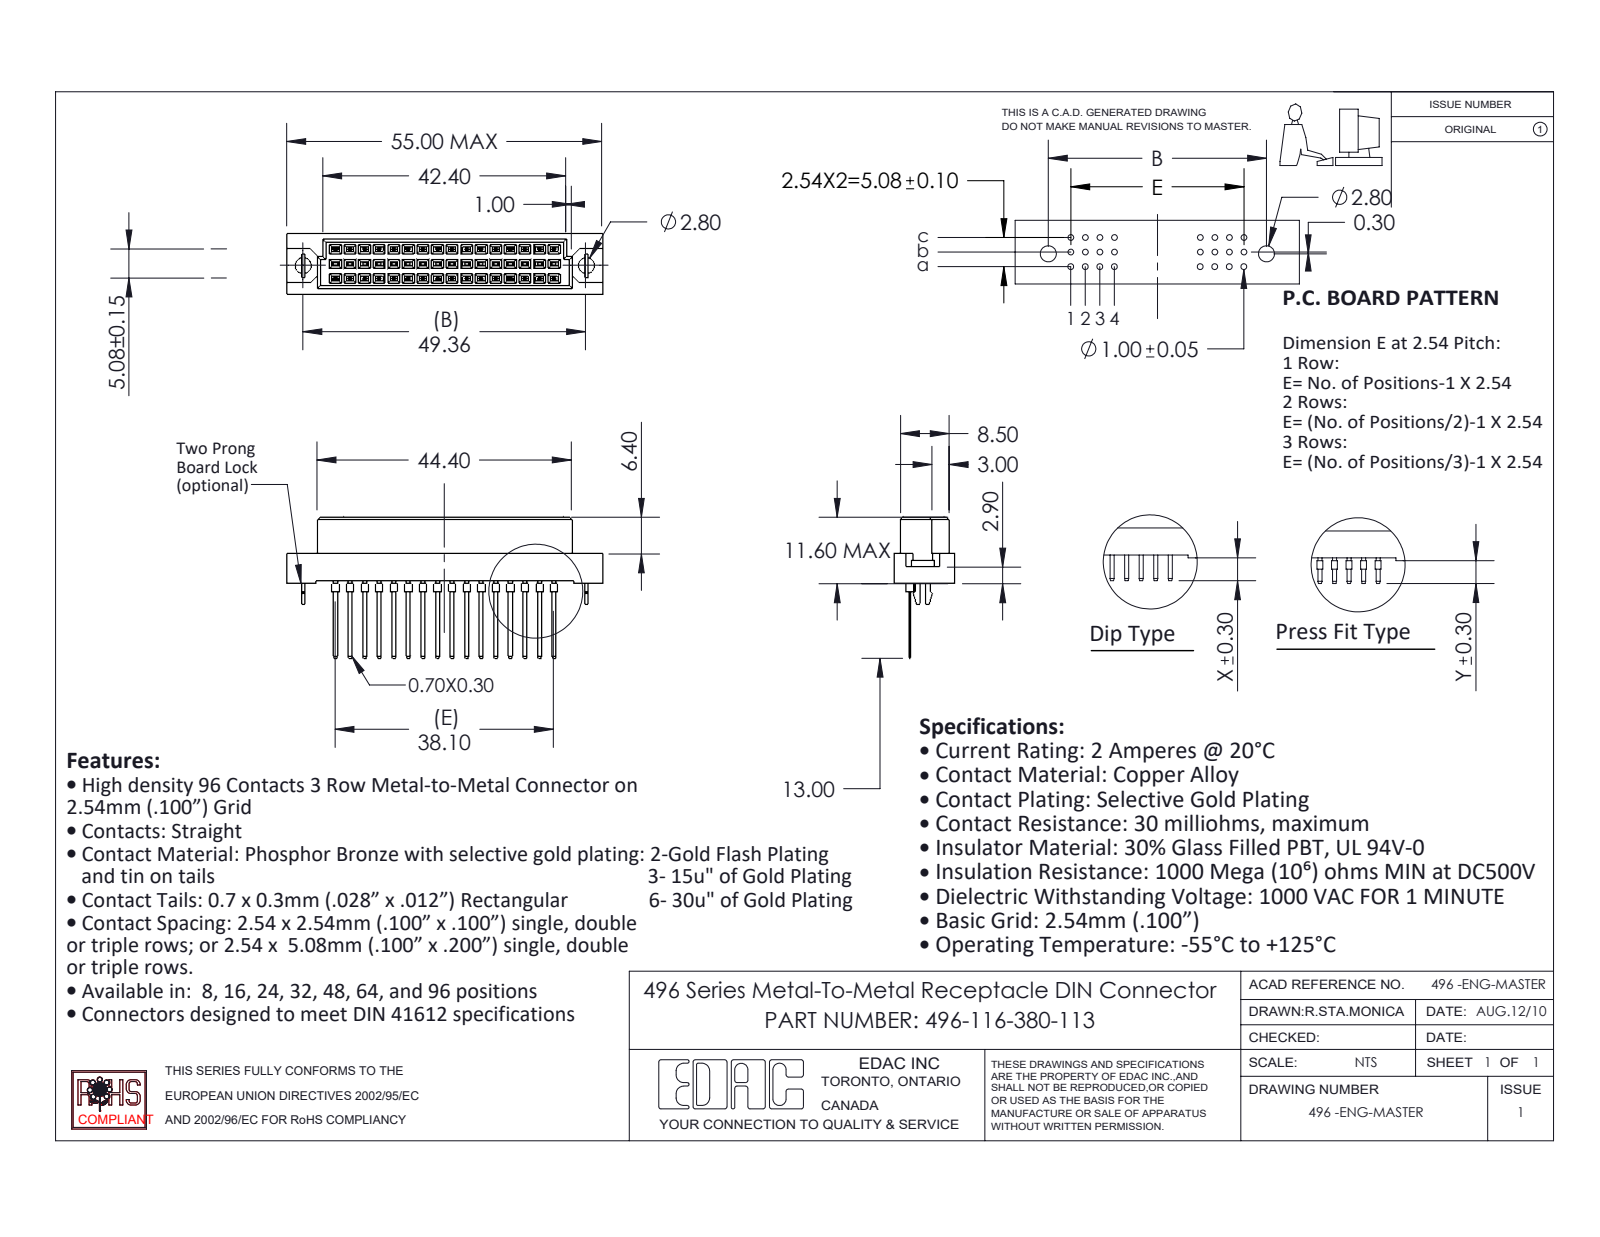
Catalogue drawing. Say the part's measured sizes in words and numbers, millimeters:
The part is named "496 Bore-lock; 496-290_80; 496-116-380-113; 496 Part_48". Its 3-D file was written by "SolidWorks 2020 (CONFIG_CONTROL_DESIGN)". It is 19 solids with 990 faces: 952 planar, 38 cylindrical and 0 other. Overall it measures 55 by 24.6 by 10.6 millimeters. Its volume is 4 684 cubic millimeters and its surface area 4 935 square millimeters. Round holes: 2 of diameter 2.8. Round bosses or shafts: 16 of diameter 1. Partial cylindrical surfaces (rounded edges, fillets, slot ends): 1 of radius 0.53. The main face-to-face distances are 2.54, 1.05, 9.55, 5.08, 0.81, 1.56, 1.86, 2.61, 2.91, 7.69. The hole center spacings are 49.36.
